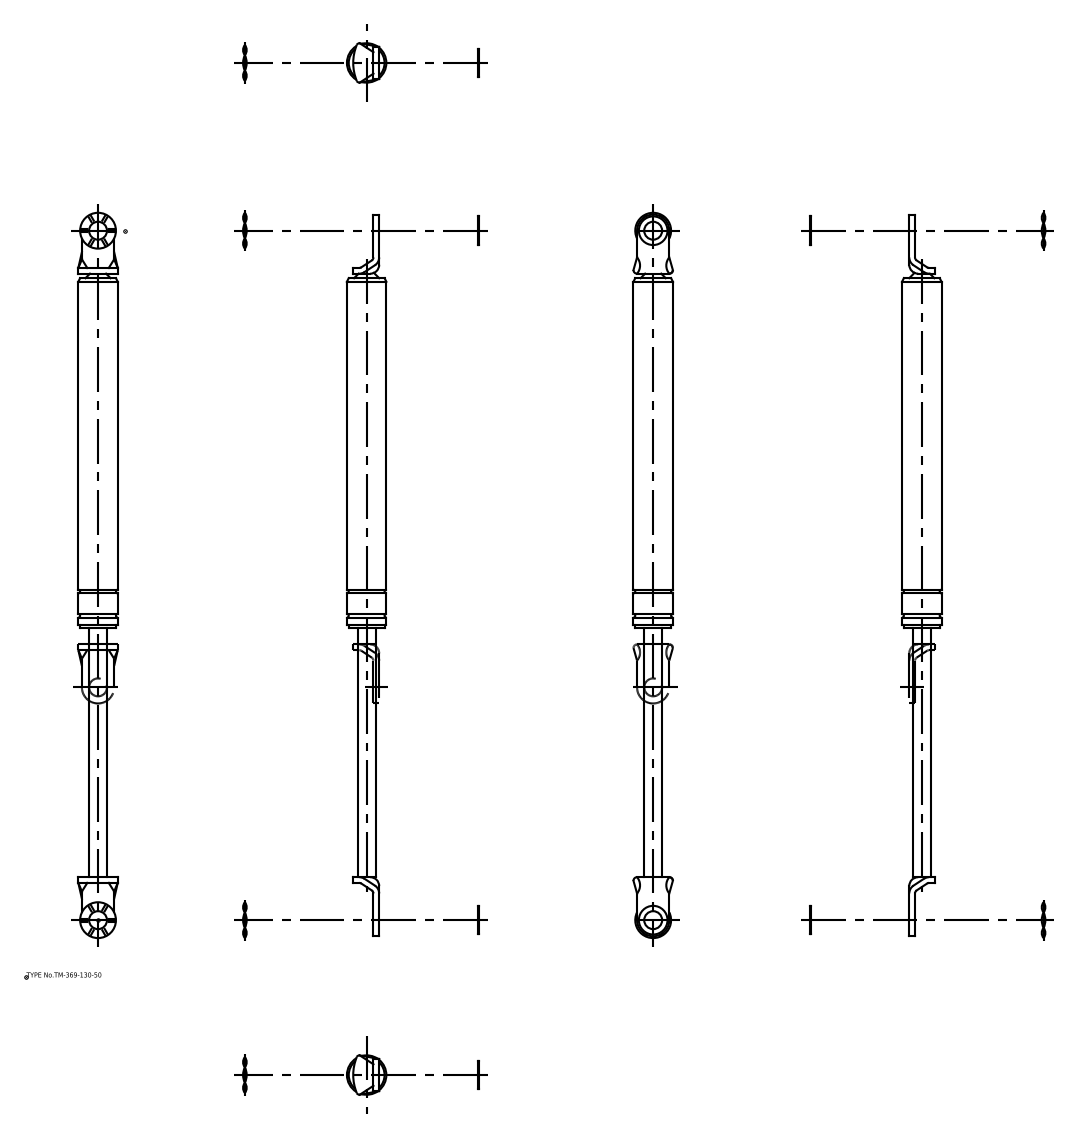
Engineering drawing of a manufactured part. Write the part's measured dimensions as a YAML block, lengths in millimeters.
part_name: "ウェーブワッシャー; ワッシャー; 本体; 本体_div"
step_written_by: "spGate 16.7.1 (AUTOMOTIVE_DESIGN)"
units: millimeters
bodies: {solids: 6, faces: 95, planar: 43, cylindrical: 44, other: 8}
overall_size: [405, 22.5, 22.5]
volume: 90925
surface_area: 24335
round_holes:
  - {diameter: 10, count: 2}
round_bosses_or_shafts:
  - {diameter: 20, count: 3}
  - {diameter: 16, count: 2}
  - {diameter: 22.5, count: 1}
  - {diameter: 22, count: 1}
  - {diameter: 10, count: 1}
partial_cylinders:
  - {radius: 4.4, count: 2}
  - {radius: 5, count: 2}
  - {radius: 9, count: 2}
  - {radius: 26.32, count: 1}
face_to_face_distances: [3.2, 2, 5.2, 5.7, 340.2, 3.7, 0.5, 201.2, 142.2, 343.4]
hole_center_spacings: [385]
